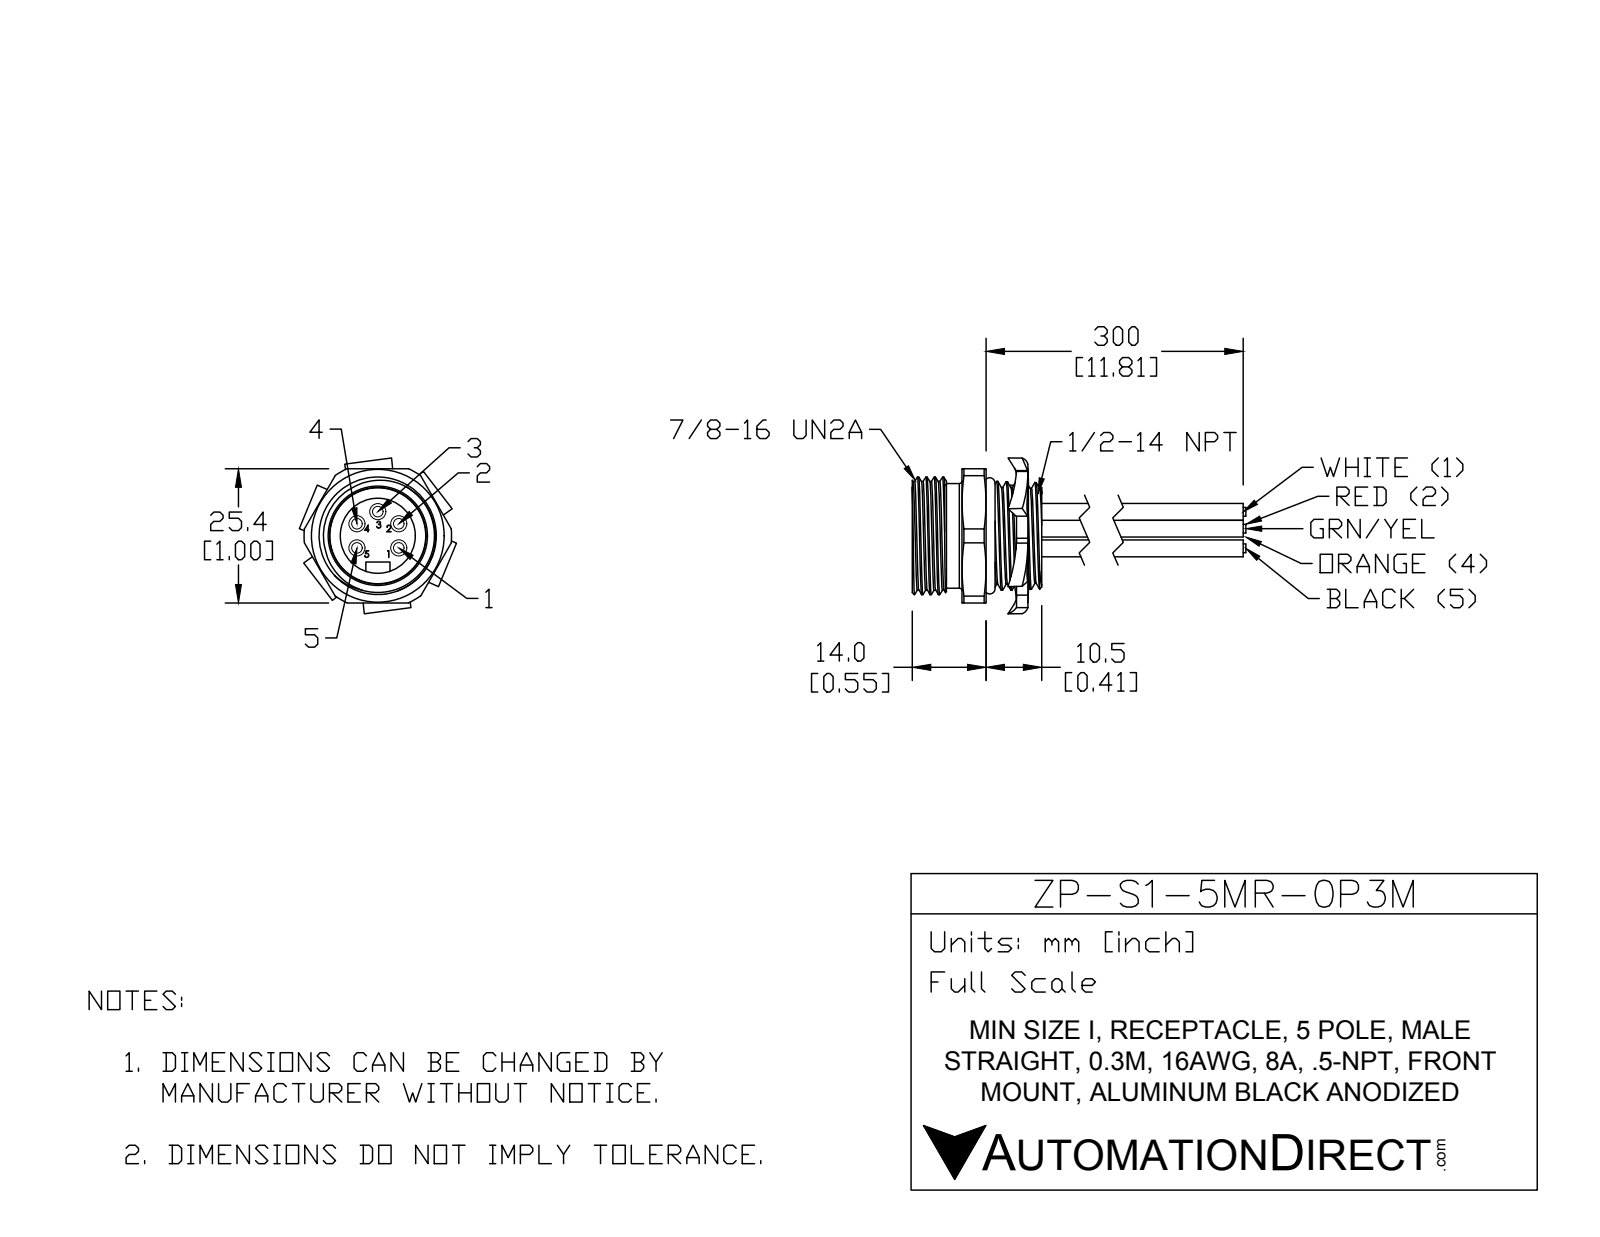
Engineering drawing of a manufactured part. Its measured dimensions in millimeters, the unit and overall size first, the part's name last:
Units: millimetres
Overall size (bounding box): 49.91 × 29.77 × 29.48
Round holes (diameter × count): ⌀14.22 ×1, ⌀18.29 ×1, ⌀19.61 ×1
Round bosses / shafts (diameter × count): ⌀3.18 ×5, ⌀3.05 ×5, ⌀2 ×5, ⌀25.37 ×1, ⌀22.22 ×1, ⌀20.6 ×1, ⌀19.81 ×1, ⌀18.14 ×1
Partial cylindrical surfaces — rounded edges, fillets, slot ends (radius × count): R2.29 ×1, R13.97 ×1
Main face-to-face distances: 25.4, 6.35, 12.37, 15.11, 4.57, 10.54, 1.45, 6.02, 16.56, 7.8
Volume: 9 322 mm³ · Surface area: 6 918 mm²
Bodies: 1 solid, 272 faces (89 planar, 81 cylindrical, 102 other)
Part name (STEP PRODUCT): MIN-5MR-ZZ
STEP written by: SolidWorks 2015 (AUTOMOTIVE_DESIGN)
